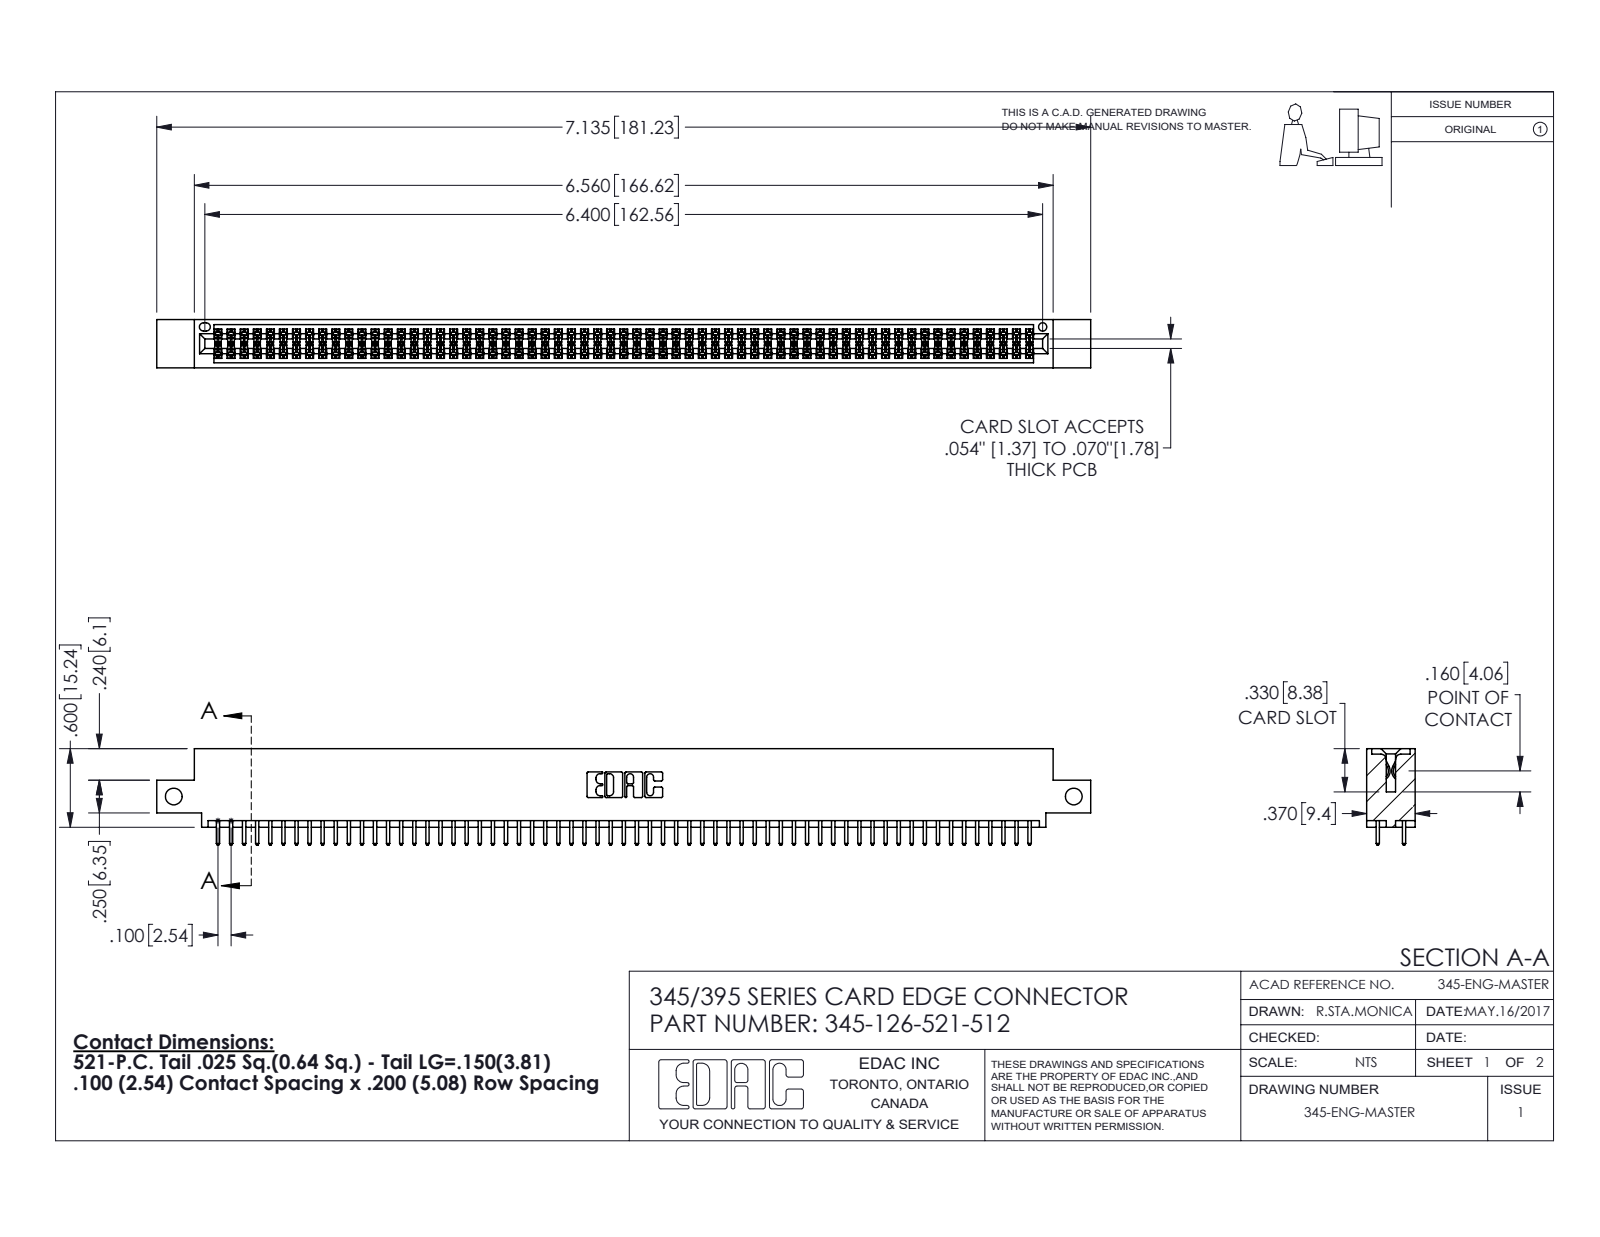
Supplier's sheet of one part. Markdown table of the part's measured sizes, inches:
| quantity | value |
| --- | --- |
| part name | 345-126-521-512; 345-292-001_345-293-121; 345 Part_0.110 Offset - Side Mount |
| STEP written by | SolidWorks 2016 (CONFIG_CONTROL_DESIGN) |
| units | inches |
| bodies | 127 solids, 6430 faces (4242 planar, 2188 cylindrical, 0 other) |
| overall size | 7.135 × 0.737 × 0.37 |
| volume | 1.073 in³ |
| surface area | 40.34 in² |
| round holes (diameter × count) | 0.128 × 2, 0.064 × 1 |
| partial cylindrical surfaces (radius × count) | 0.006 × 189, 0.01 × 126, 0.01 × 22, 0.007 × 6, 0.031 × 6, 0.026 × 3, 0.014 × 2, 0.019 × 2 |
| main face-to-face distances | 0.298, 0.072, 0.2, 0.098, 0.272, 0.025, 0.37, 0.225, 0.175, 0.149 |
| hole center spacings | 6.875 |
